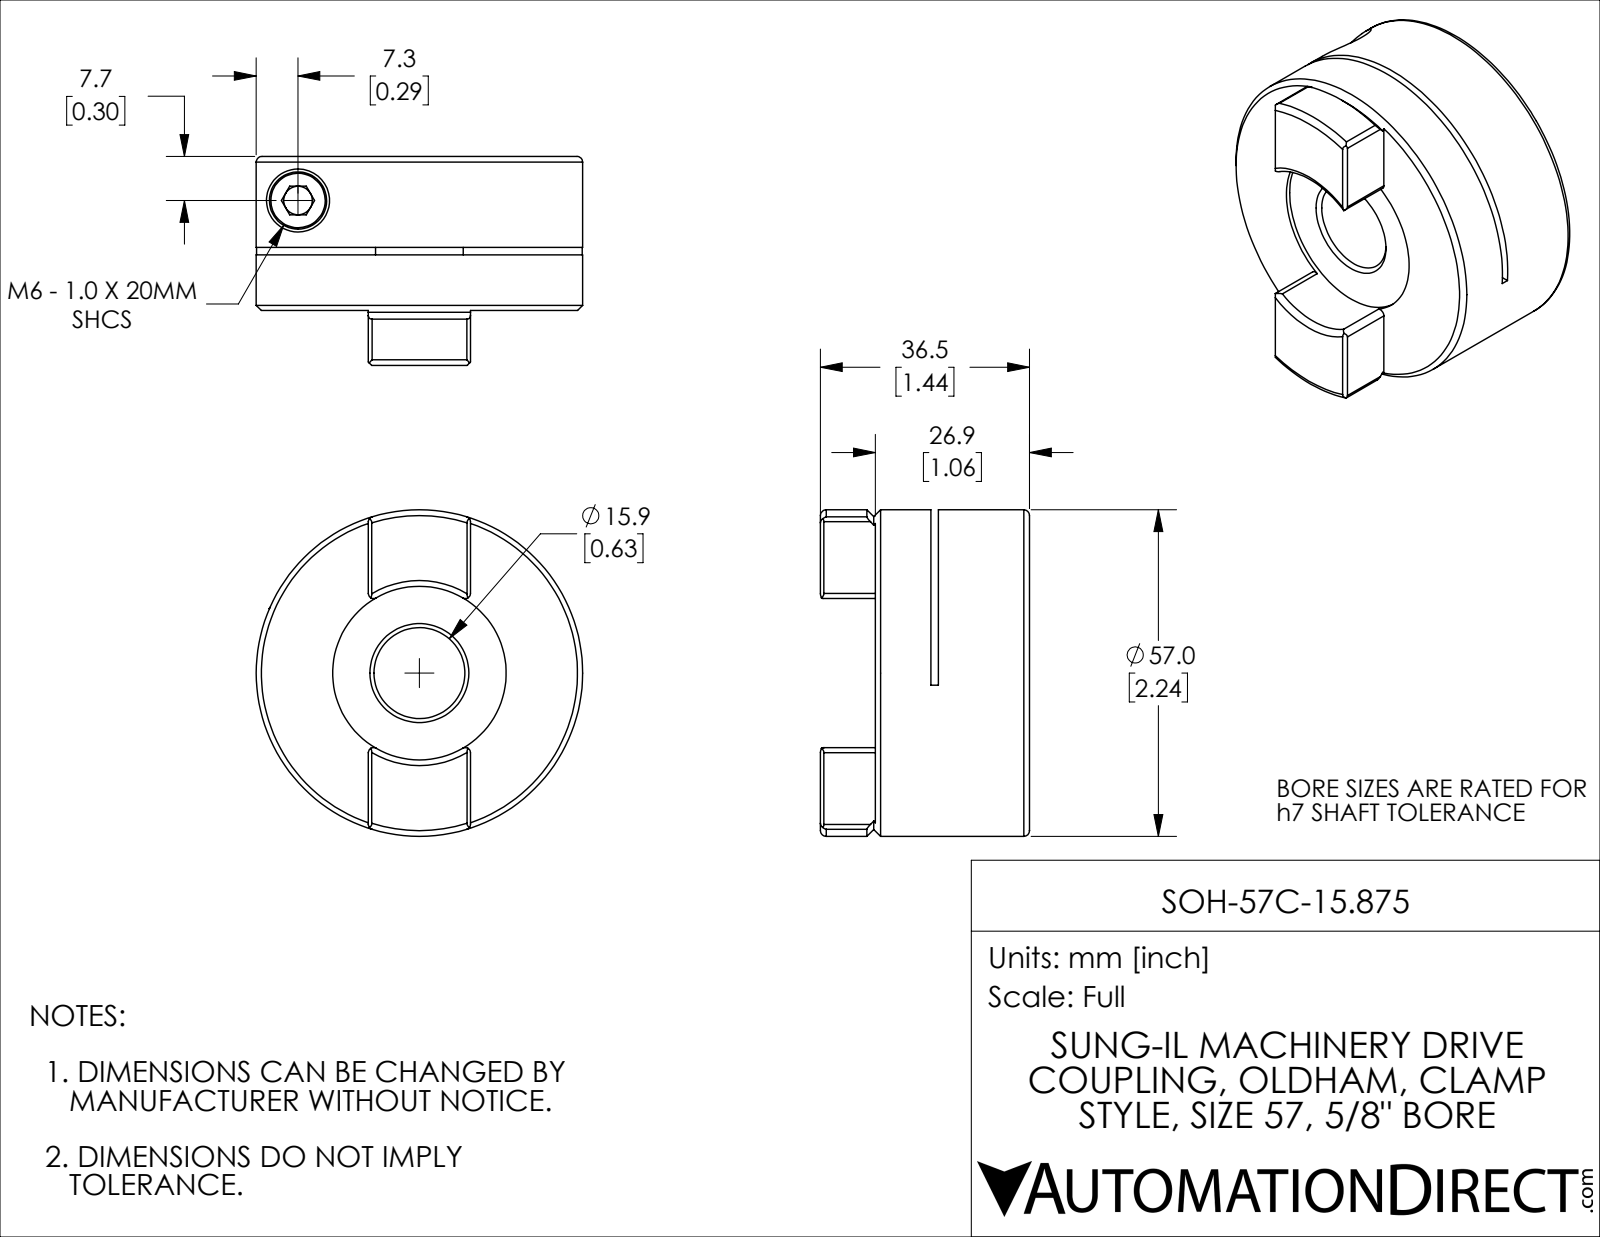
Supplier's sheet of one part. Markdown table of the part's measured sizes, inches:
| quantity | value |
| --- | --- |
| part name | SOH-57C-15.875 |
| STEP written by | SolidWorks 2021 (CONFIG_CONTROL_DESIGN) |
| units | inches |
| bodies | 2 solids, 100 faces (39 planar, 33 cylindrical, 28 other) |
| overall size | 2.244 × 2.244 × 1.437 |
| volume | 3.927 in³ |
| surface area | 25.65 in² |
| round holes (diameter × count) | 0.197 × 1, 0.252 × 1, 0.433 × 1, 0.625 × 1, 1.193 × 1 |
| round bosses / shafts (diameter × count) | 2.244 × 1, 0.394 × 1, 0.236 × 1 |
| partial cylindrical surfaces (radius × count) | 0.035 × 8, 1.575 × 1 |
| main face-to-face distances | 0.051, 0.677, 0.626, 1.059, 0.433, 0.382, 0.402, 1.028, 0.35, 0.031 |
